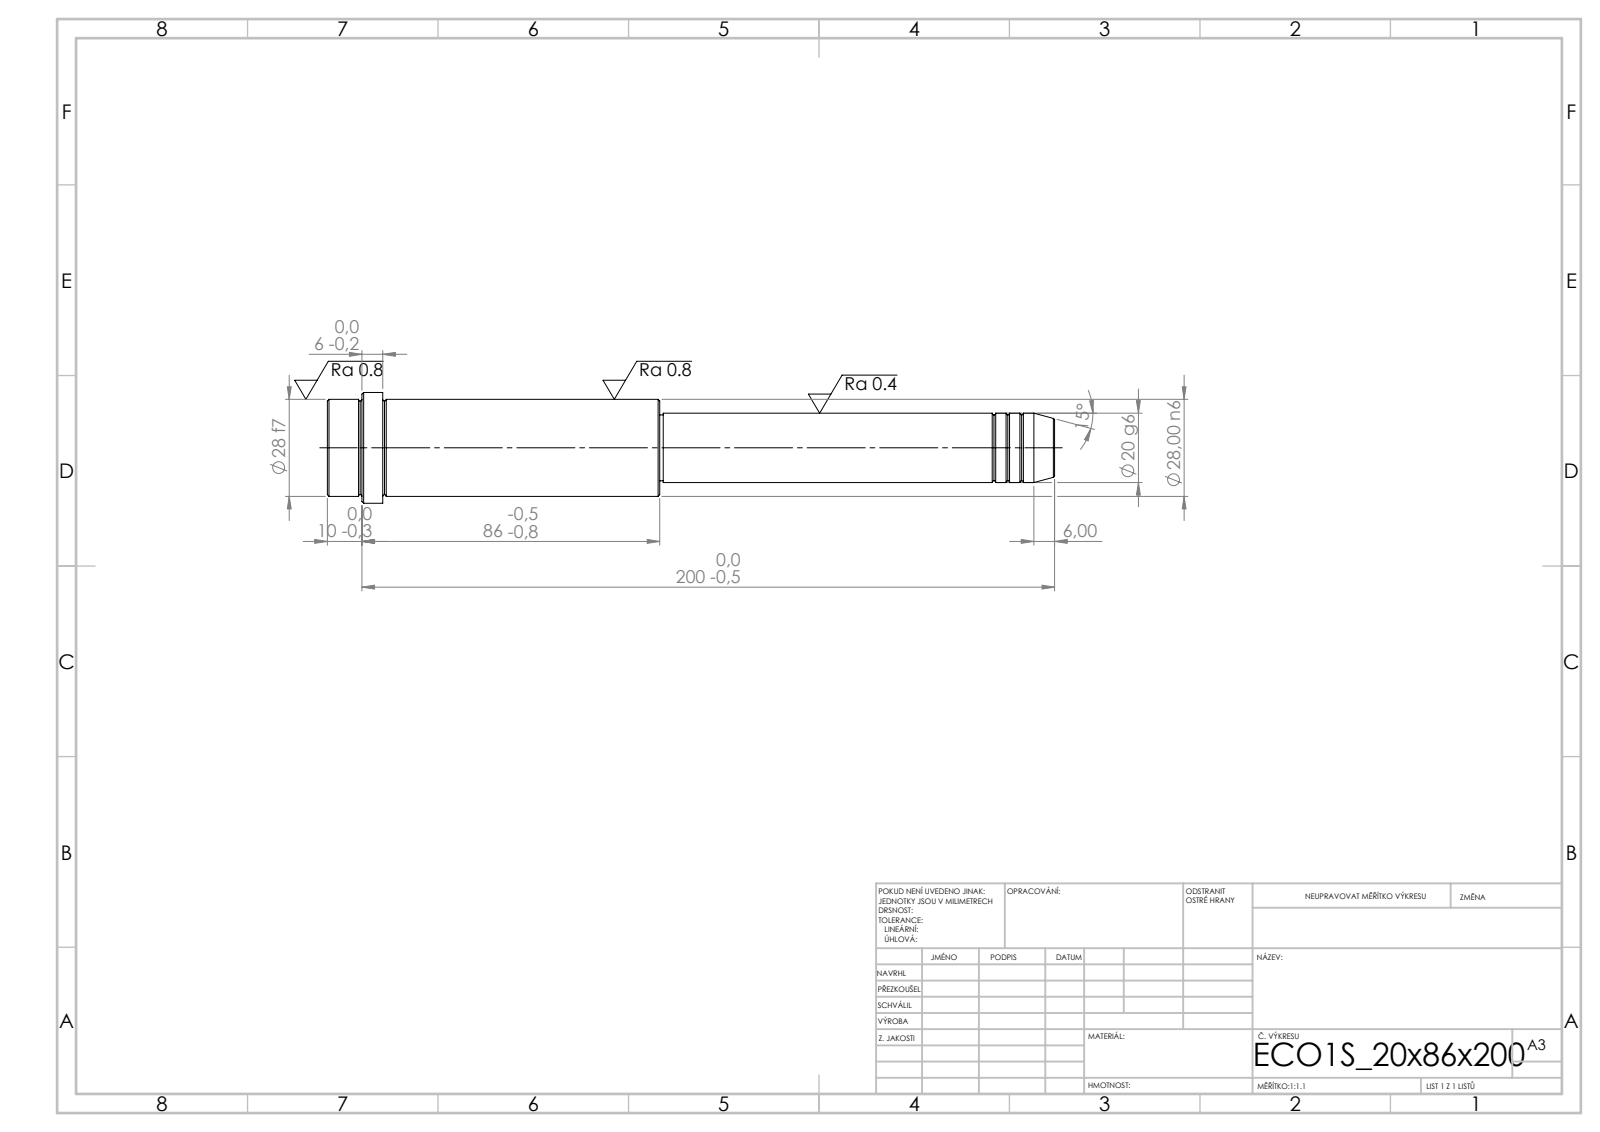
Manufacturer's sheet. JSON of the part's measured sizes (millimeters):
{"step_written_by": "SolidWorks 2019 (CONFIG_CONTROL_DESIGN)", "units": "millimeters", "bodies": {"solids": 1, "faces": 52, "planar": 6, "cylindrical": 16, "other": 30}, "overall_size": [210, 32, 32], "volume_mm3": 95564, "surface_area_mm2": 17343, "round_bosses_or_shafts": [[32, 1], [28, 1], [20, 1], [19, 1]], "face_to_face_distances": [96, 114, 210, 194, 80, 16, 200, 86, 6, 10]}
